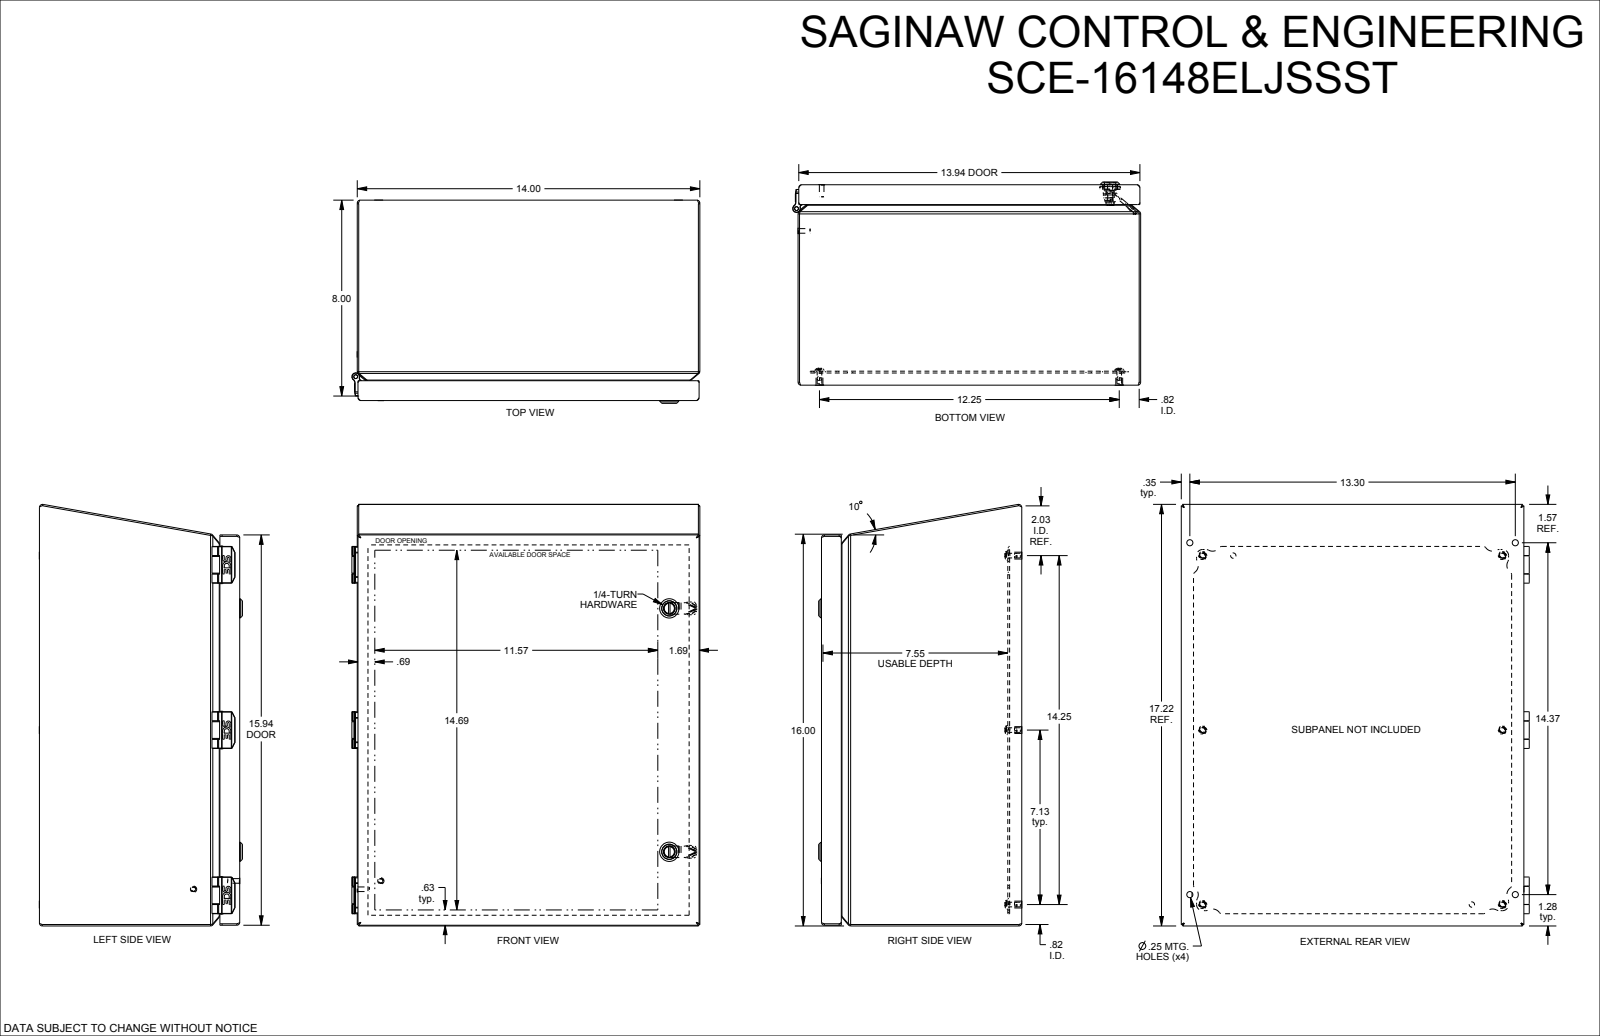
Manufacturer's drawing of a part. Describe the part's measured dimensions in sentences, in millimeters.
The part is named "SCE-16148ELJSSST". Its 3-D file was written by "SolidWorks 2021 (AUTOMOTIVE_DESIGN)". It is 51 solids with 2157 faces: 855 planar, 508 cylindrical and 794 other. Overall it measures 437.2 by 361.2 by 210.7 millimeters. Its volume is 1 295 000 cubic millimeters and its surface area 1 612 000 square millimeters. Round holes: 6 of diameter 4.1, 6 of diameter 4.8, 6 of diameter 6.4, 4 of diameter 7.2, 3 of diameter 0.5, 3 of diameter 2.5, 2 of diameter 5.1, 2 of diameter 5.5, 2 of diameter 6.1, 2 of diameter 6.5, 2 of diameter 6.8, 2 of diameter 6.8. Round bosses or shafts: 8 of diameter 4.8, 6 of diameter 12.3, 6 of diameter 9.5, 6 of diameter 7.1, 6 of diameter 6, 6 of diameter 4.1, 3 of diameter 6.6, 3 of diameter 4.6. Partial cylindrical surfaces (rounded edges, fillets, slot ends): 62 of radius 0.8, 36 of radius 0.2, 31 of radius 0.3, 18 of radius 0.3, 13 of radius 6.4, 12 of radius 1.5, 11 of radius 3.2, 9 of radius 1.6. The main face-to-face distances are 1.5, 1.5, 354.1, 207.9, 206.4, 206.4, 204.9, 14.5, 13, 191.9. The hole center spacings are 171.5, 342.9, 181, 359.9, 311.2, 0.5, 16.8, 25.9.
